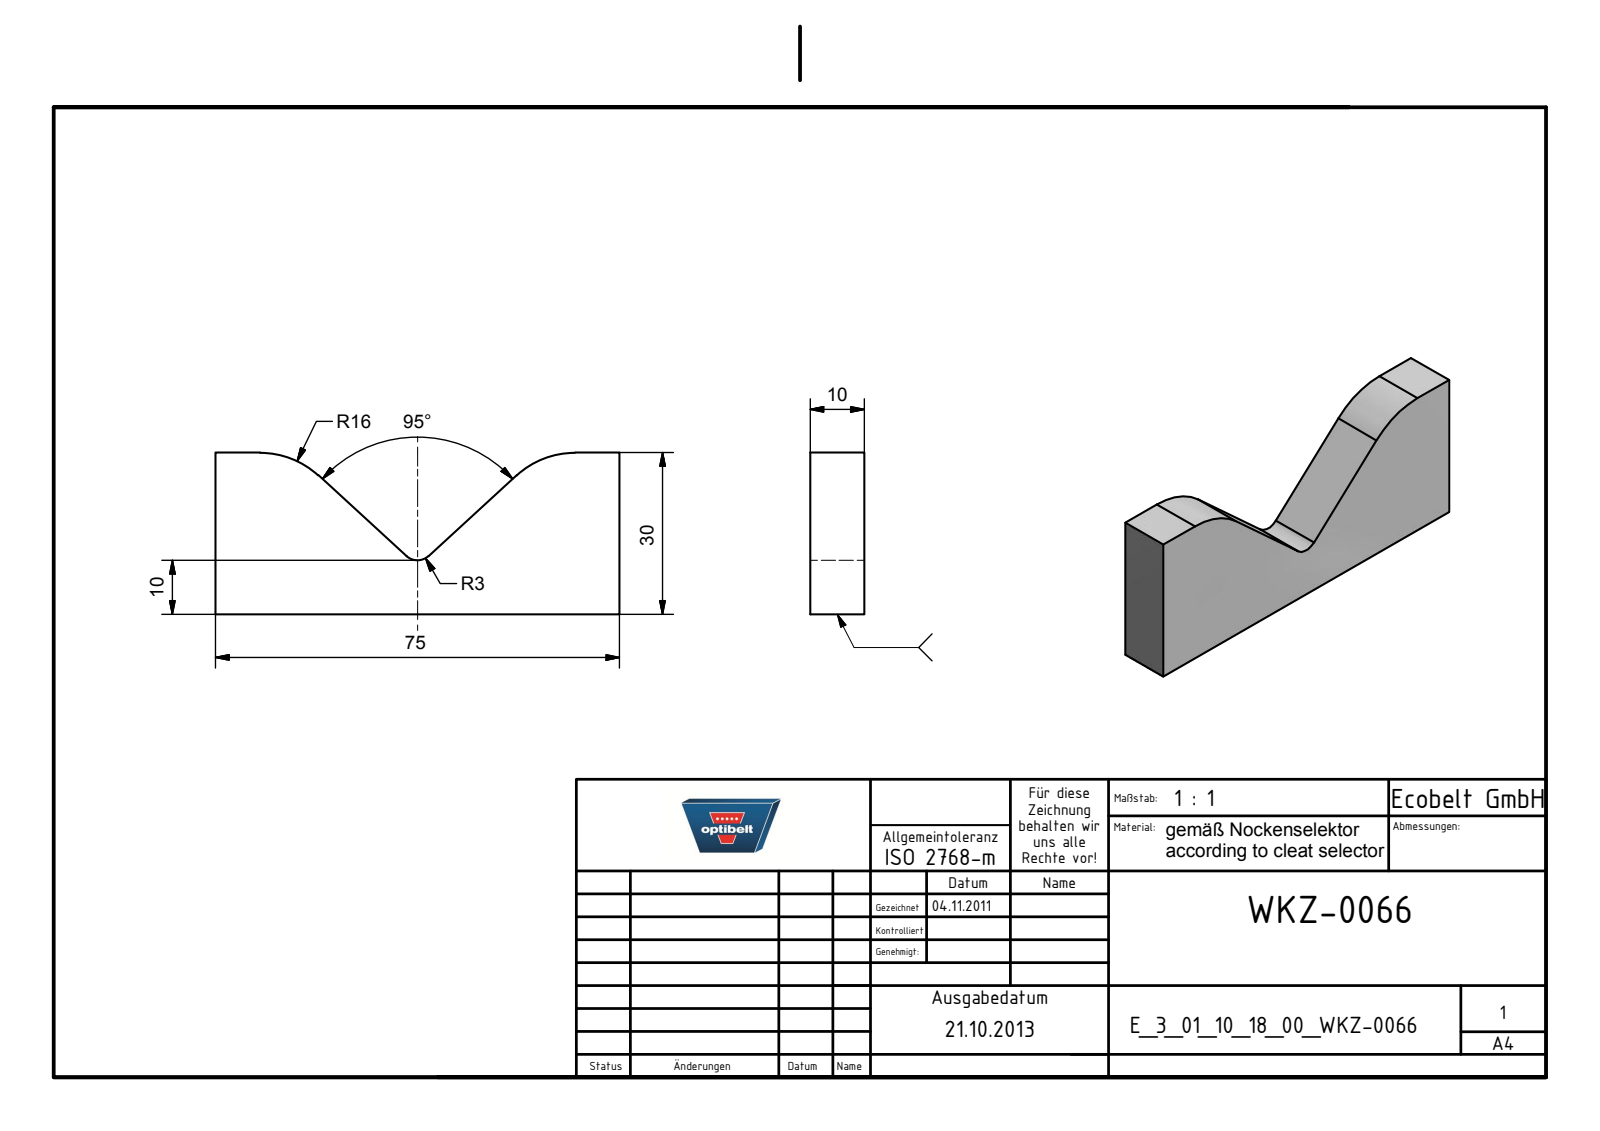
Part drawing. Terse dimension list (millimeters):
name: E_3_01_10_18_00_WKZ-0066
written by: Autodesk Inventor 2025 (AUTOMOTIVE_DESIGN)
unit: mm
bodies: 1 solid, 12 faces (9 planar, 3 cylindrical, 0 other)
size: 75 × 30 × 10
volume: 17 579 mm³; area: 5 758 mm²
rounds: 2× R16, 1× R3
face distances: 10, 75, 30
